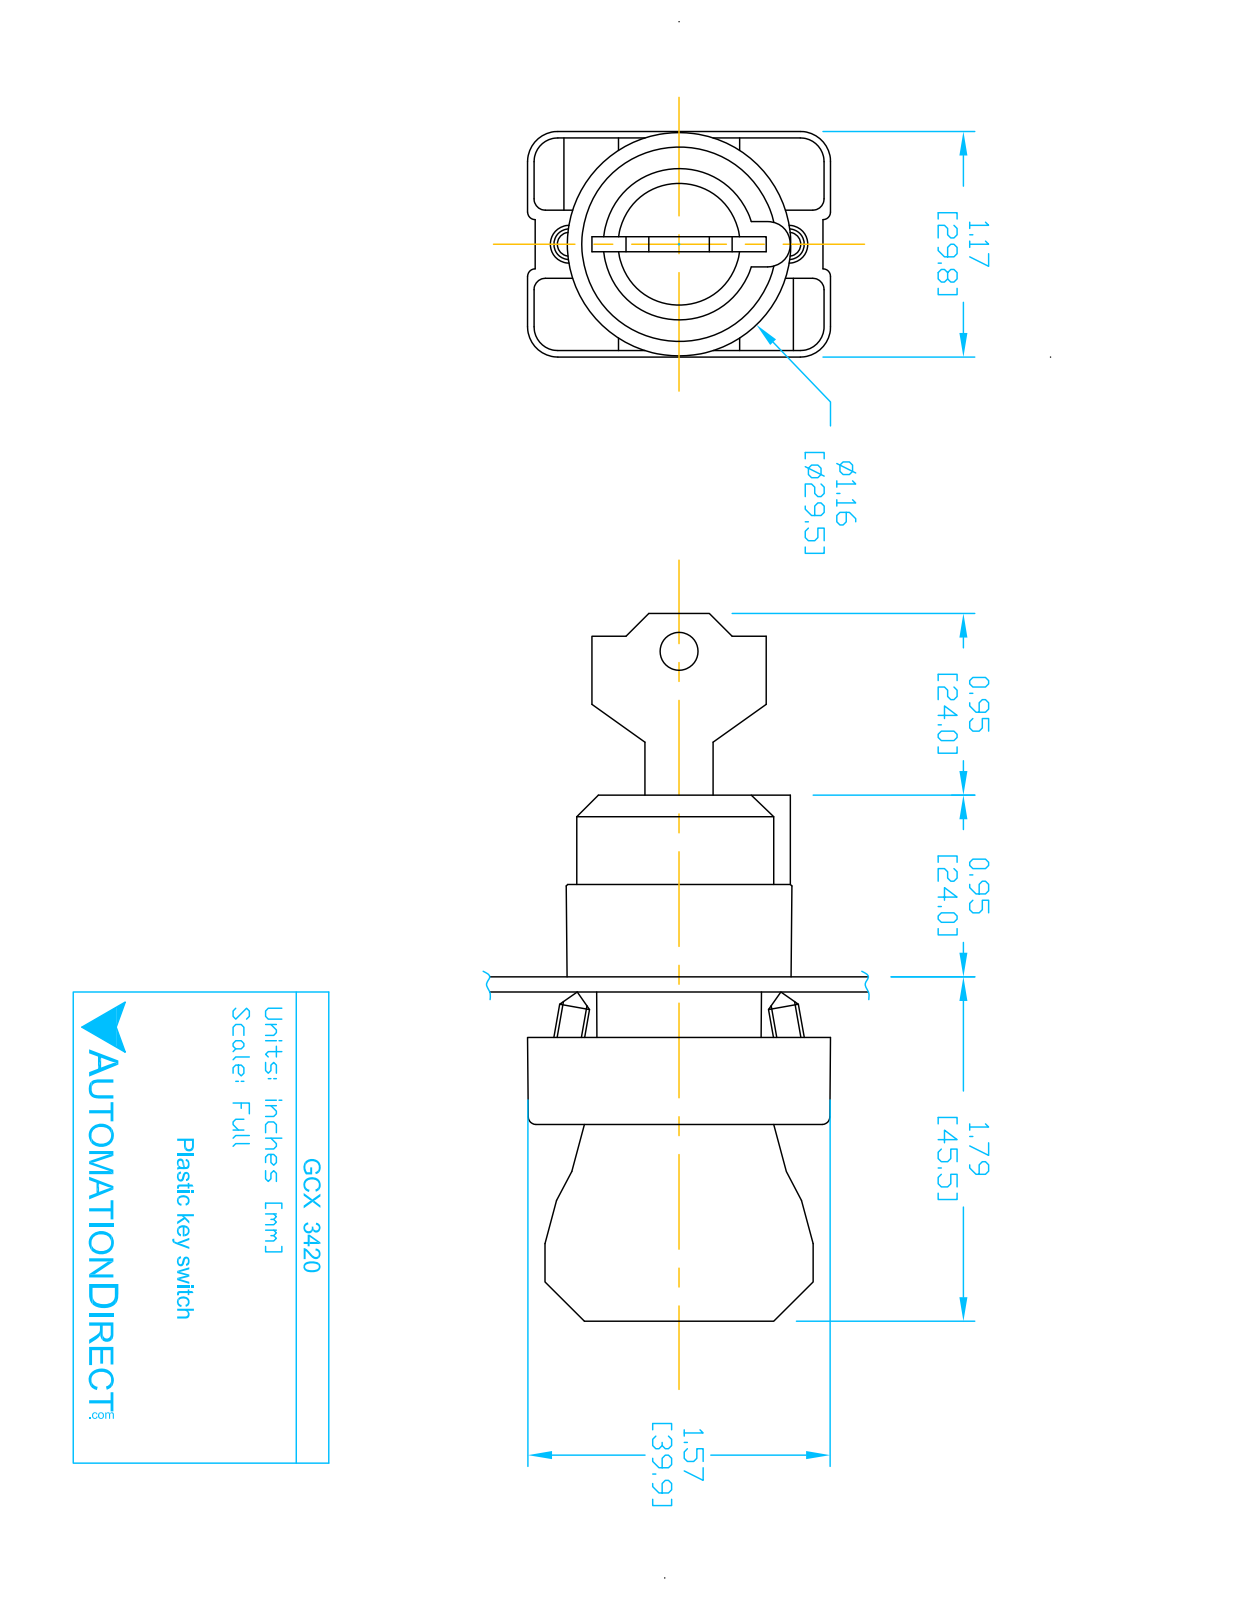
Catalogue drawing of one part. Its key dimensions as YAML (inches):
part_name: "GCX3420; ecx1040; ECX3029-2; GCX3420 OPERATOR"
step_written_by: "SolidWorks 2016 (AUTOMOTIVE_DESIGN)"
units: inches
bodies: {solids: 7, faces: 405, planar: 235, cylindrical: 142, other: 28}
overall_size: [2.651, 1.581, 1.177]
volume: 2.007
surface_area: 32.29
round_holes:
  - {diameter: 0.079, count: 2}
  - {diameter: 0.124, count: 2}
  - {diameter: 0.13, count: 2}
  - {diameter: 0.087, count: 1}
  - {diameter: 0.197, count: 1}
  - {diameter: 0.591, count: 1}
  - {diameter: 0.878, count: 1}
  - {diameter: 0.888, count: 1}
  - {diameter: 1.024, count: 1}
round_bosses_or_shafts:
  - {diameter: 0.157, count: 2}
  - {diameter: 1.175, count: 1}
  - {diameter: 1.004, count: 1}
  - {diameter: 0.965, count: 1}
  - {diameter: 0.945, count: 1}
  - {diameter: 0.856, count: 1}
  - {diameter: 0.78, count: 1}
  - {diameter: 0.571, count: 1}
partial_cylinders:
  - {radius: 0.059, count: 24}
  - {radius: 0.041, count: 12}
  - {radius: 0.124, count: 12}
  - {radius: 0.157, count: 12}
  - {radius: 0.039, count: 6}
  - {radius: 0.128, count: 2}
  - {radius: 0.02, count: 1}
  - {radius: 0.063, count: 1}
face_to_face_distances: [0.72, 0.579, 0.033, 0.031, 0.689, 0.598, 0.539, 0.638, 0.578, 0.122]
hole_center_spacings: [0.236, 0.544, 0.472, 0.49]
